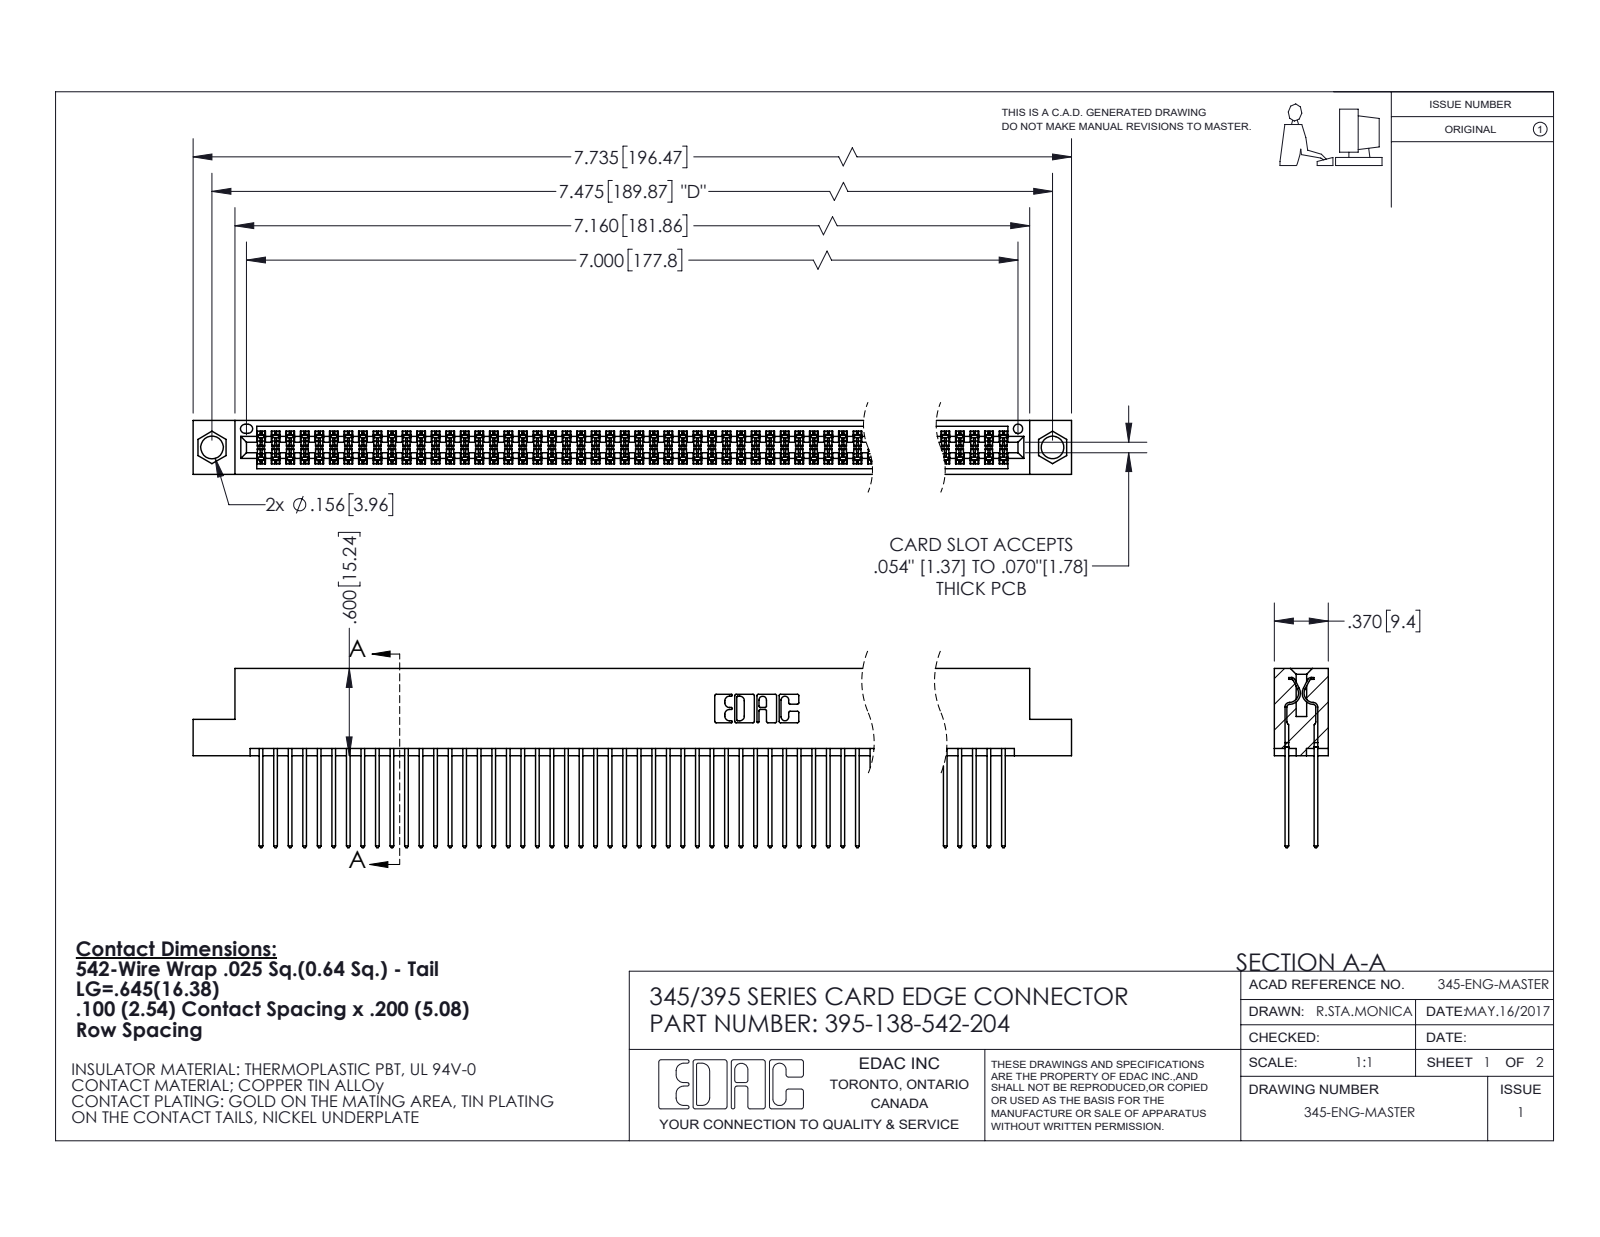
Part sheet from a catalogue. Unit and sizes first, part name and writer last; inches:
Units: inches
Overall size (bounding box): 7.735 × 1.232 × 0.37
Round holes (diameter × count): ⌀0.156 ×2, ⌀0.064 ×1
Partial cylindrical surfaces — rounded edges, fillets, slot ends (radius × count): R0.006 ×207, R0.01 ×138, R0.01 ×22, R0.007 ×6, R0.031 ×6, R0.026 ×3, R0.014 ×2, R0.019 ×2
Main face-to-face distances: 0.072, 0.298, 0.2, 0.098, 0.272, 0.025, 0.225, 0.37, 0.175, 0.149
Hole centre spacings: 0.27, 7.239, 7.475
Volume: 1.213 in³ · Surface area: 50.77 in²
Bodies: 139 solids, 7040 faces (4648 planar, 2392 cylindrical, 0 other)
Part name (STEP PRODUCT): 345 Part_Flush Mounting Lugs - 0.156 Dia-TI; 395-138-542-204; 345-292-001_345-293-142
STEP written by: SolidWorks 2020 (CONFIG_CONTROL_DESIGN)
